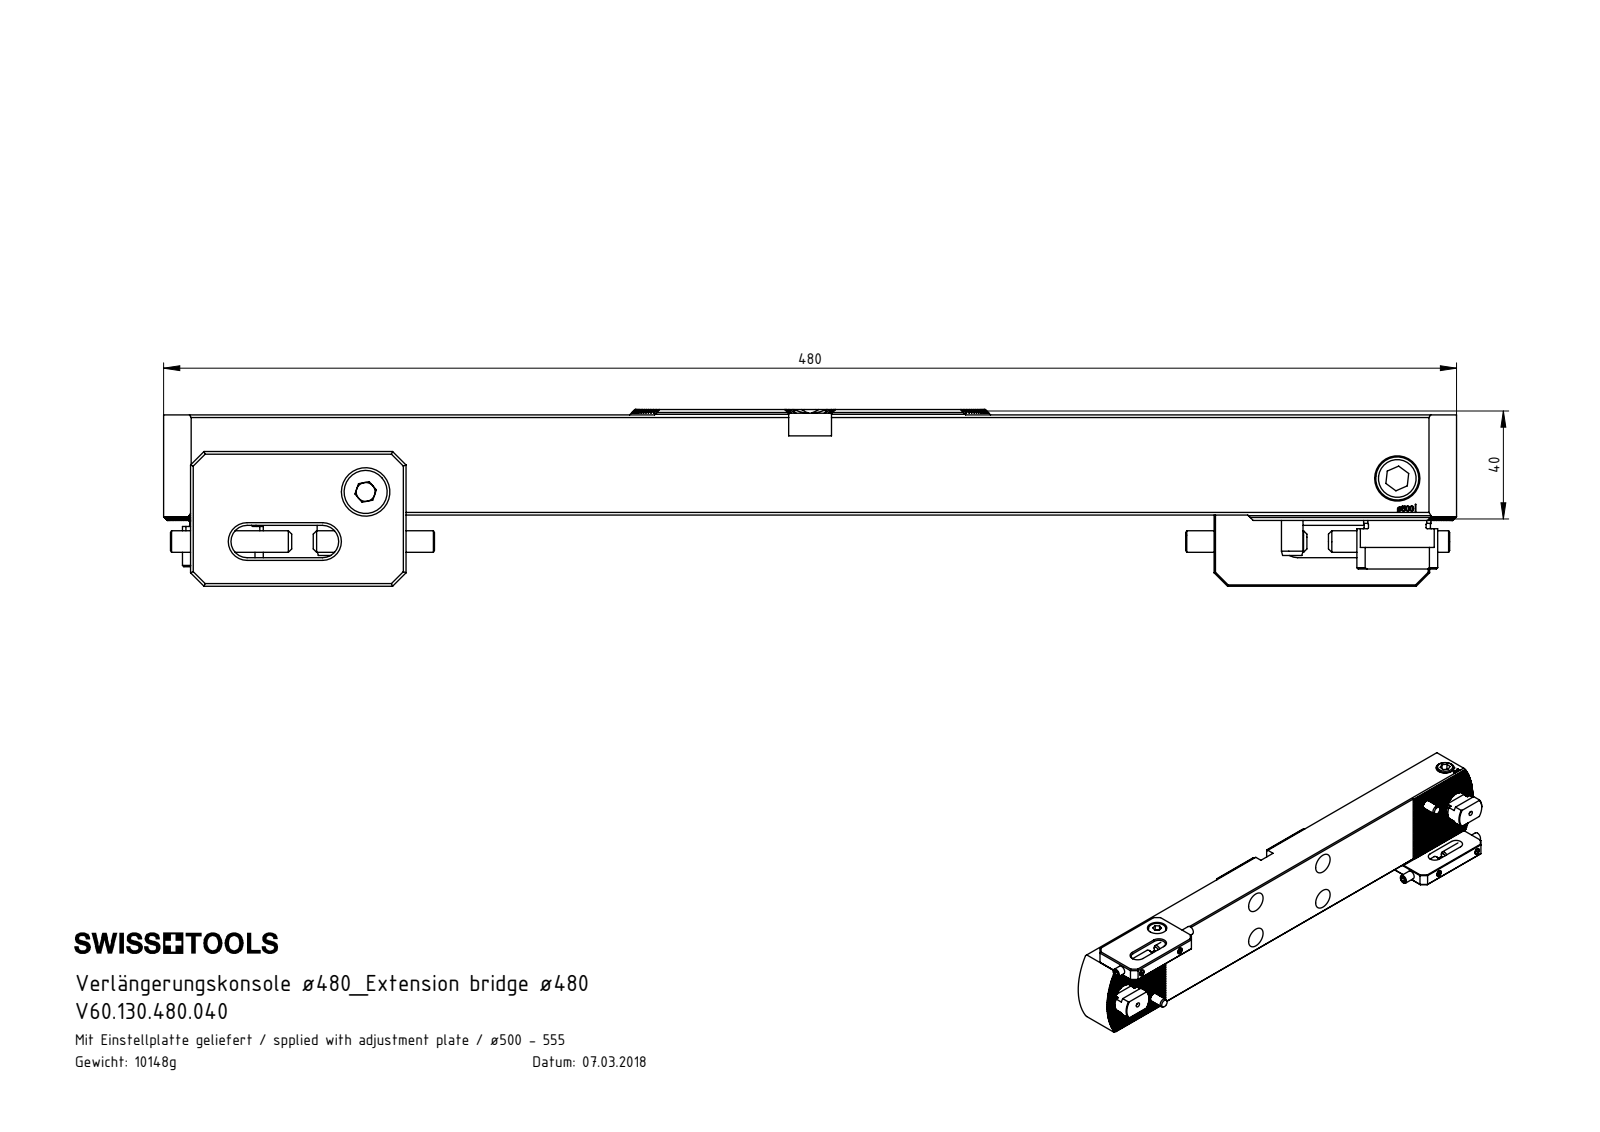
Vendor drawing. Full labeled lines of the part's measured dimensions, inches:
Part name (STEP PRODUCT): VK1-ER7.001.012_mit langer Schraube; VK1-ER2.201.010_A_gespannt; VK1-ER2.001.044_A; ISO 4766 - M6x12_ISO 4766 - M6 x 10 (+8 more)
STEP written by: SolidWorks 2017 (AUTOMOTIVE_DESIGN)
Units: inches
Bodies: 27 solids, 1319 faces (862 planar, 260 cylindrical, 197 other)
Overall size (bounding box): 18.898 × 3.701 × 2.582
Volume: 79.27 in³ · Surface area: 290.5 in²
Round holes (diameter × count): ⌀0.197 ×4, ⌀0.236 ×4, ⌀0.268 ×4, ⌀0.512 ×4, ⌀0.748 ×4, ⌀0.079 ×2, ⌀0.315 ×2, ⌀0.335 ×2, ⌀0.413 ×2, ⌀0.433 ×2, ⌀0.551 ×2, ⌀0.709 ×2
Round bosses / shafts (diameter × count): ⌀0.63 ×4, ⌀0.236 ×4, ⌀0.394 ×2, ⌀0.315 ×2
Partial cylindrical surfaces — rounded edges, fillets, slot ends (radius × count): R0.006 ×66, R0.079 ×8, R0.236 ×4, R0.484 ×2, R0.591 ×2, R2.559 ×2, R0.313 ×1
Main face-to-face distances: 1.463, 2.756, 0.472, 3.228, 0.068, 0.341, 0.136, 0.273, 0.02, 1.637
Hole centre spacings: 17.165, 6.896, 10.345, 0.311, 0.73, 0.772, 1.359, 1.381
